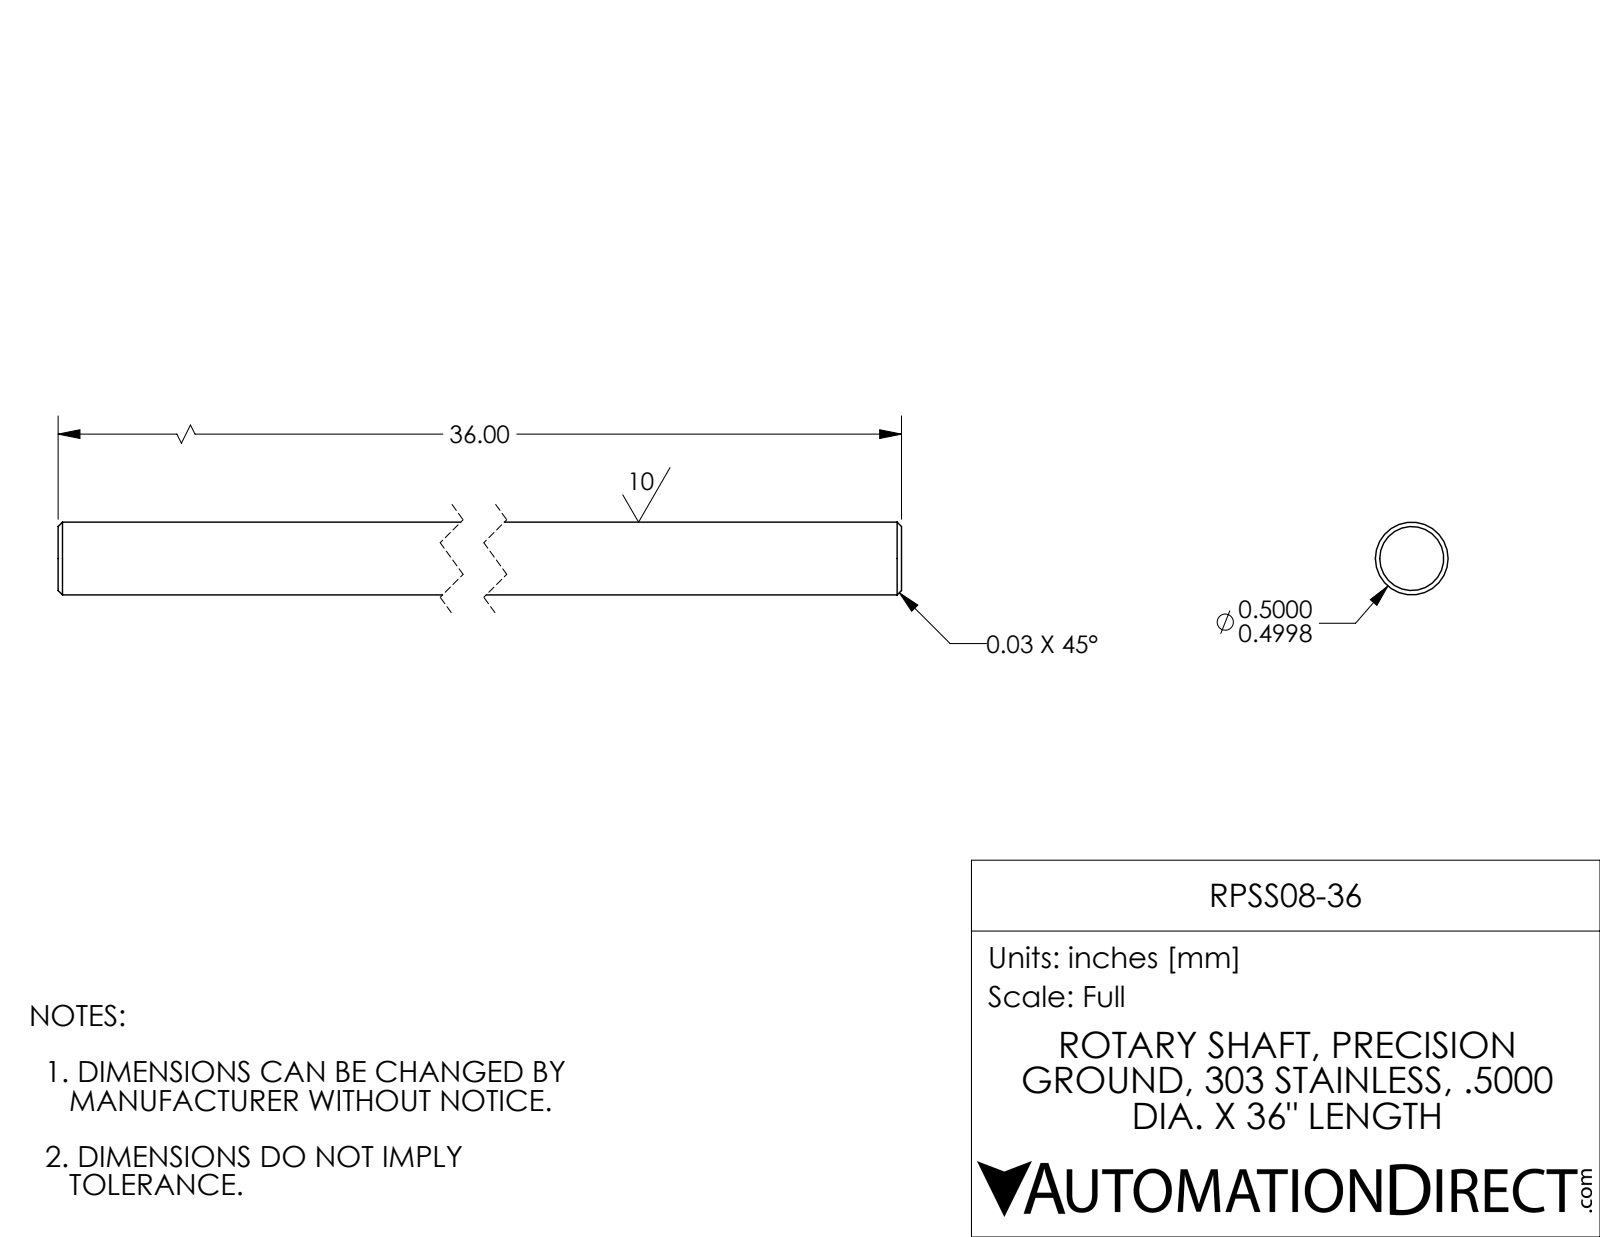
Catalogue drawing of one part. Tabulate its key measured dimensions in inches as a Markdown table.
| quantity | value |
| --- | --- |
| part name | RPSS08-36 |
| STEP written by | SolidWorks 2017 (AUTOMOTIVE_DESIGN) |
| units | inches |
| bodies | 1 solid, 8 faces (2 planar, 2 cylindrical, 4 other) |
| overall size | 36 × 0.5 × 0.5 |
| volume | 7.067 in³ |
| surface area | 56.88 in² |
| round bosses / shafts (diameter × count) | 0.5 × 1 |
| main face-to-face distances | 36 |
